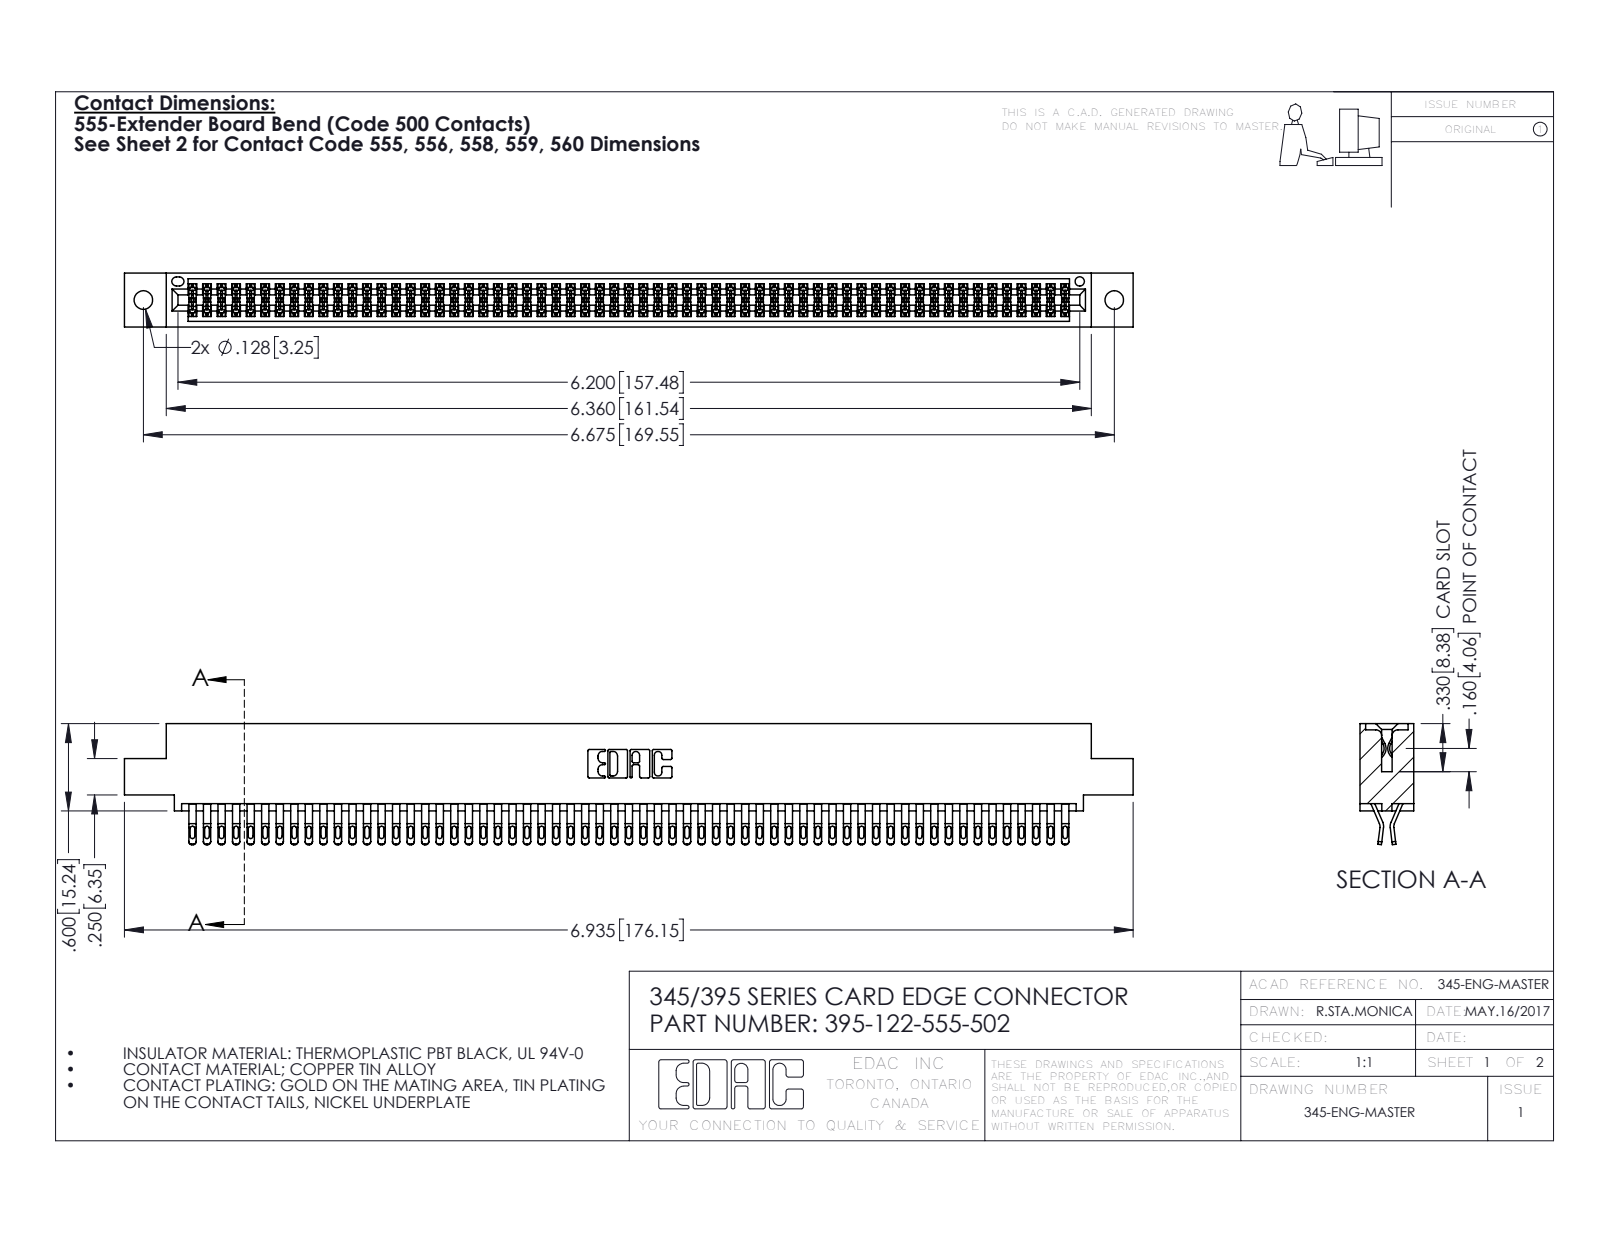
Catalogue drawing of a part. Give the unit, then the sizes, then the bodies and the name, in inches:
Units: inches
Overall size (bounding box): 6.935 × 0.832 × 0.37
Round holes (diameter × count): ⌀0.128 ×2, ⌀0.064 ×1
Partial cylindrical surfaces — rounded edges, fillets, slot ends (radius × count): R0.016 ×305, R0.02 ×244, R0.006 ×183, R0.01 ×22, R0.007 ×6, R0.031 ×6, R0.026 ×3, R0.01 ×2
Main face-to-face distances: 0.298, 0.072, 0.025, 0.37, 0.2, 0.098, 0.272, 0.225, 0.175, 0.149
Hole centre spacings: 0.27, 6.439, 6.675
Volume: 1.07 in³ · Surface area: 42.37 in²
Bodies: 123 solids, 6962 faces (3866 planar, 3096 cylindrical, 0 other)
Part name (STEP PRODUCT): 345 Part_0.110 Offset - 0.128 Dia; 395-122-555-502; 345-292-001_555 Tail
STEP written by: SolidWorks 2016 (CONFIG_CONTROL_DESIGN)
